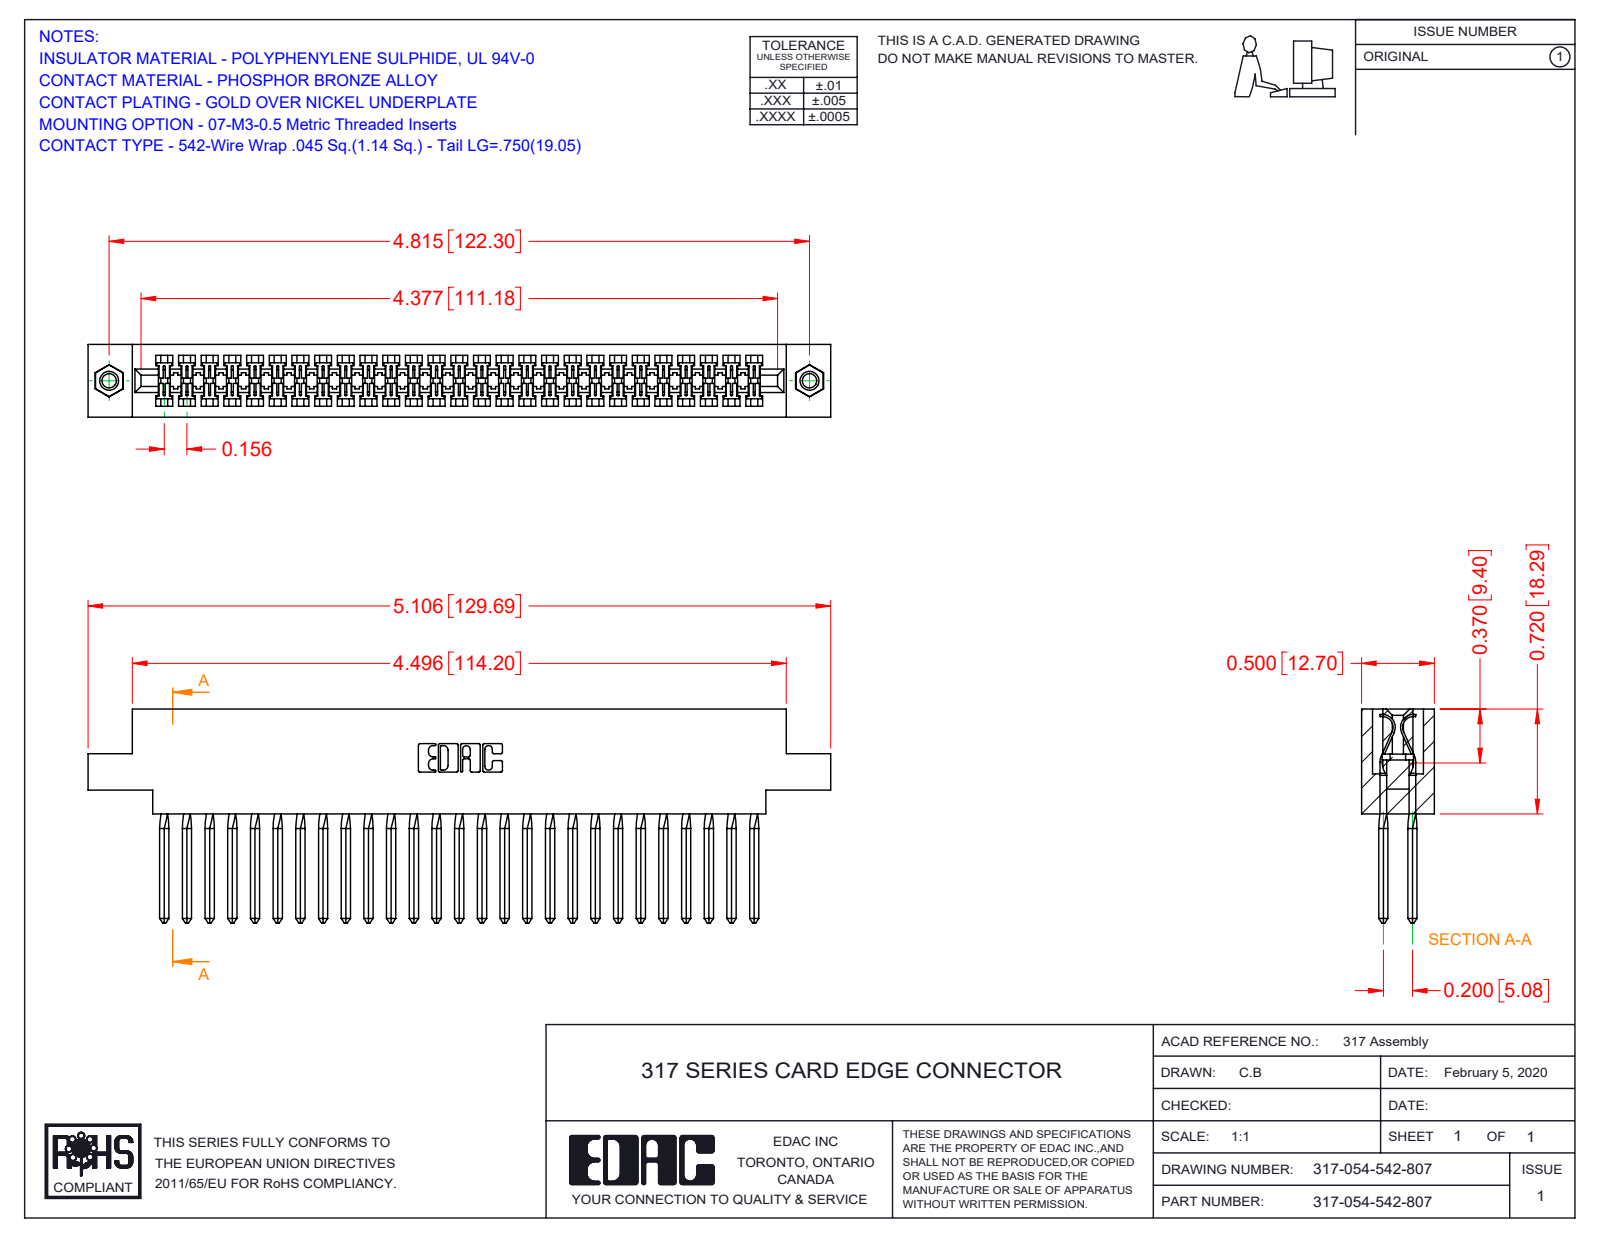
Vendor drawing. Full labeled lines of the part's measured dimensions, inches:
Part name (STEP PRODUCT): 317-290-003_542; 317 Part_.156 Dia - TI; 317-054-542-807; 345-250-001_345-250-005-103
STEP written by: SolidWorks 2016 (CONFIG_CONTROL_DESIGN)
Units: inches
Bodies: 57 solids, 3240 faces (2574 planar, 434 cylindrical, 232 other)
Overall size (bounding box): 5.106 × 1.47 × 0.5
Volume: 1.266 in³ · Surface area: 44.03 in²
Round holes (diameter × count): ⌀0.098 ×2, ⌀0.125 ×2, ⌀0.156 ×2
Round bosses / shafts (diameter × count): ⌀0.155 ×2
Partial cylindrical surfaces — rounded edges, fillets, slot ends (radius × count): R0.006 ×108, R0.01 ×22, R0.007 ×6, R0.031 ×6, R0.026 ×3, R0.074 ×2, R0.089 ×2, R0.1 ×2
Main face-to-face distances: 0.5, 0.075, 0.425, 0.35, 0.2, 0.11, 0.116, 0.046, 0.136, 0.72
Hole centre spacings: 4.815
